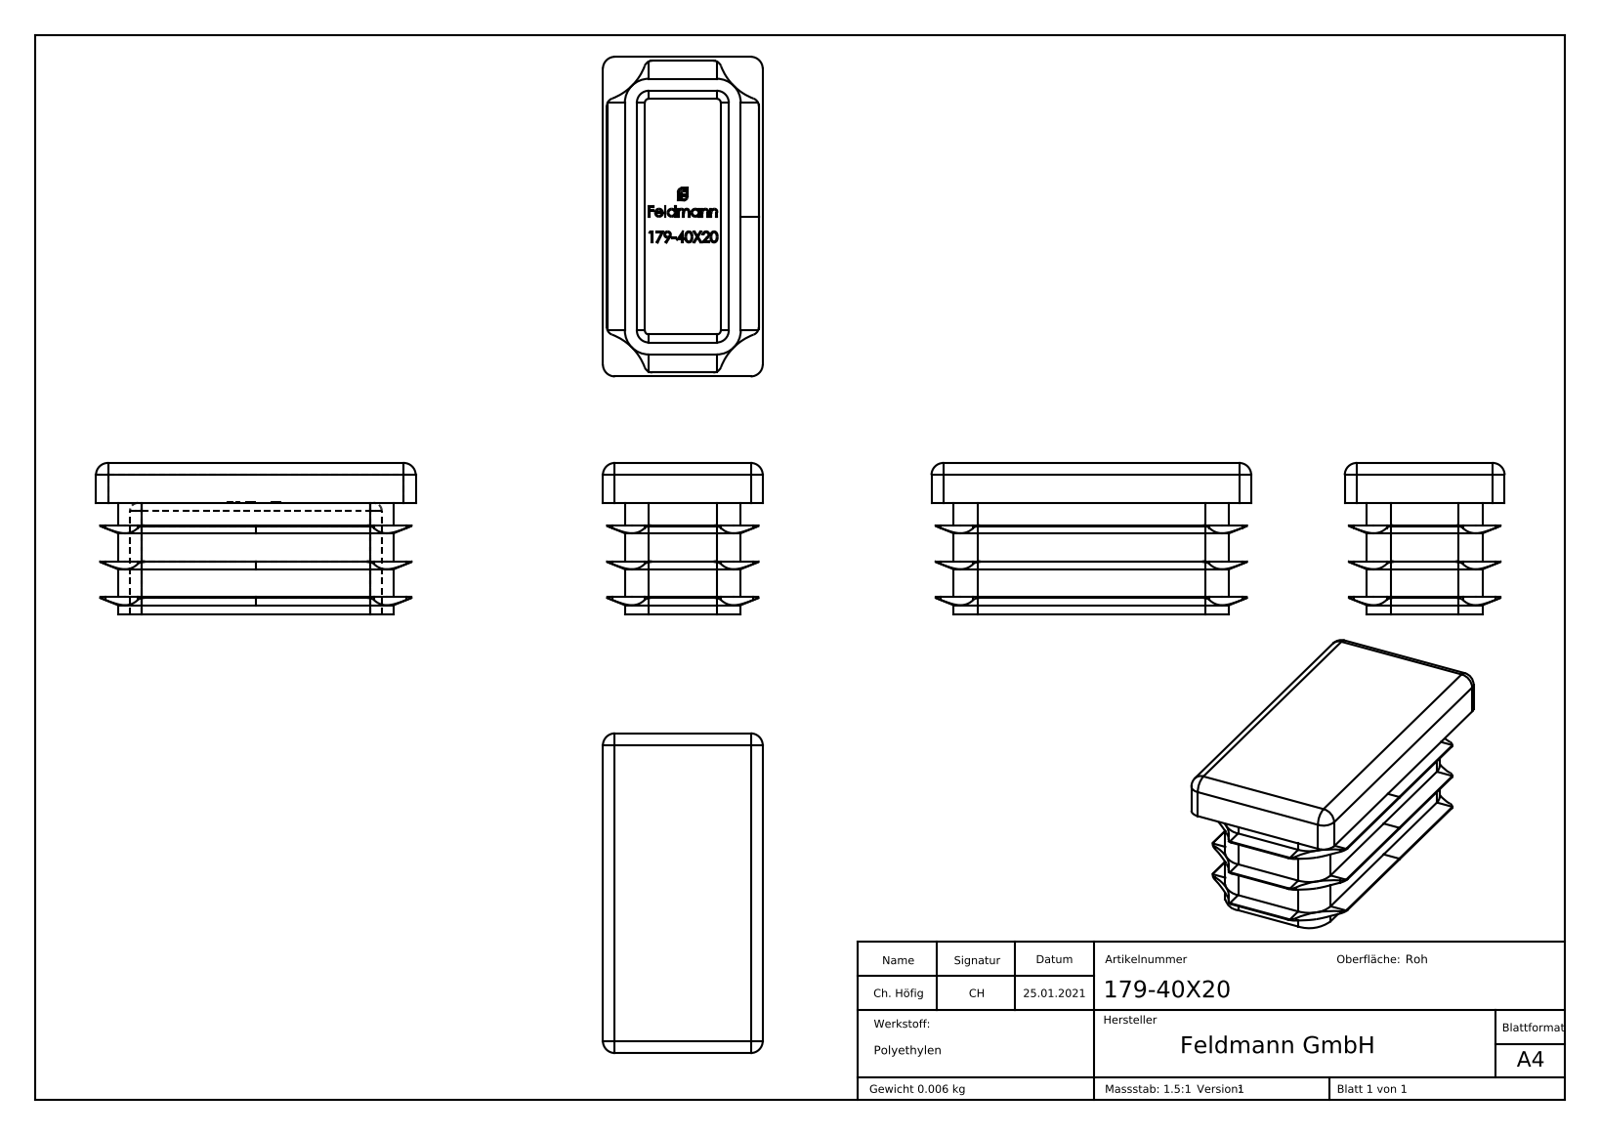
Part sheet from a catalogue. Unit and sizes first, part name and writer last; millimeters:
Units: millimetres
Overall size (bounding box): 40 × 20 × 19
Partial cylindrical surfaces — rounded edges, fillets, slot ends (radius × count): R1 ×12, R1.5 ×12, R3 ×4, R7 ×4
Main face-to-face distances: 1.5, 13, 5, 2.75, 4.25, 11.5, 4.5, 4.17, 14.5, 15.75
Volume: 6 104 mm³ · Surface area: 5 472 mm²
Bodies: 1 solid, 447 faces (231 planar, 83 cylindrical, 133 other)
Part name (STEP PRODUCT): 179-40X20
STEP written by: SolidWorks 2018 (CONFIG_CONTROL_DESIGN)
